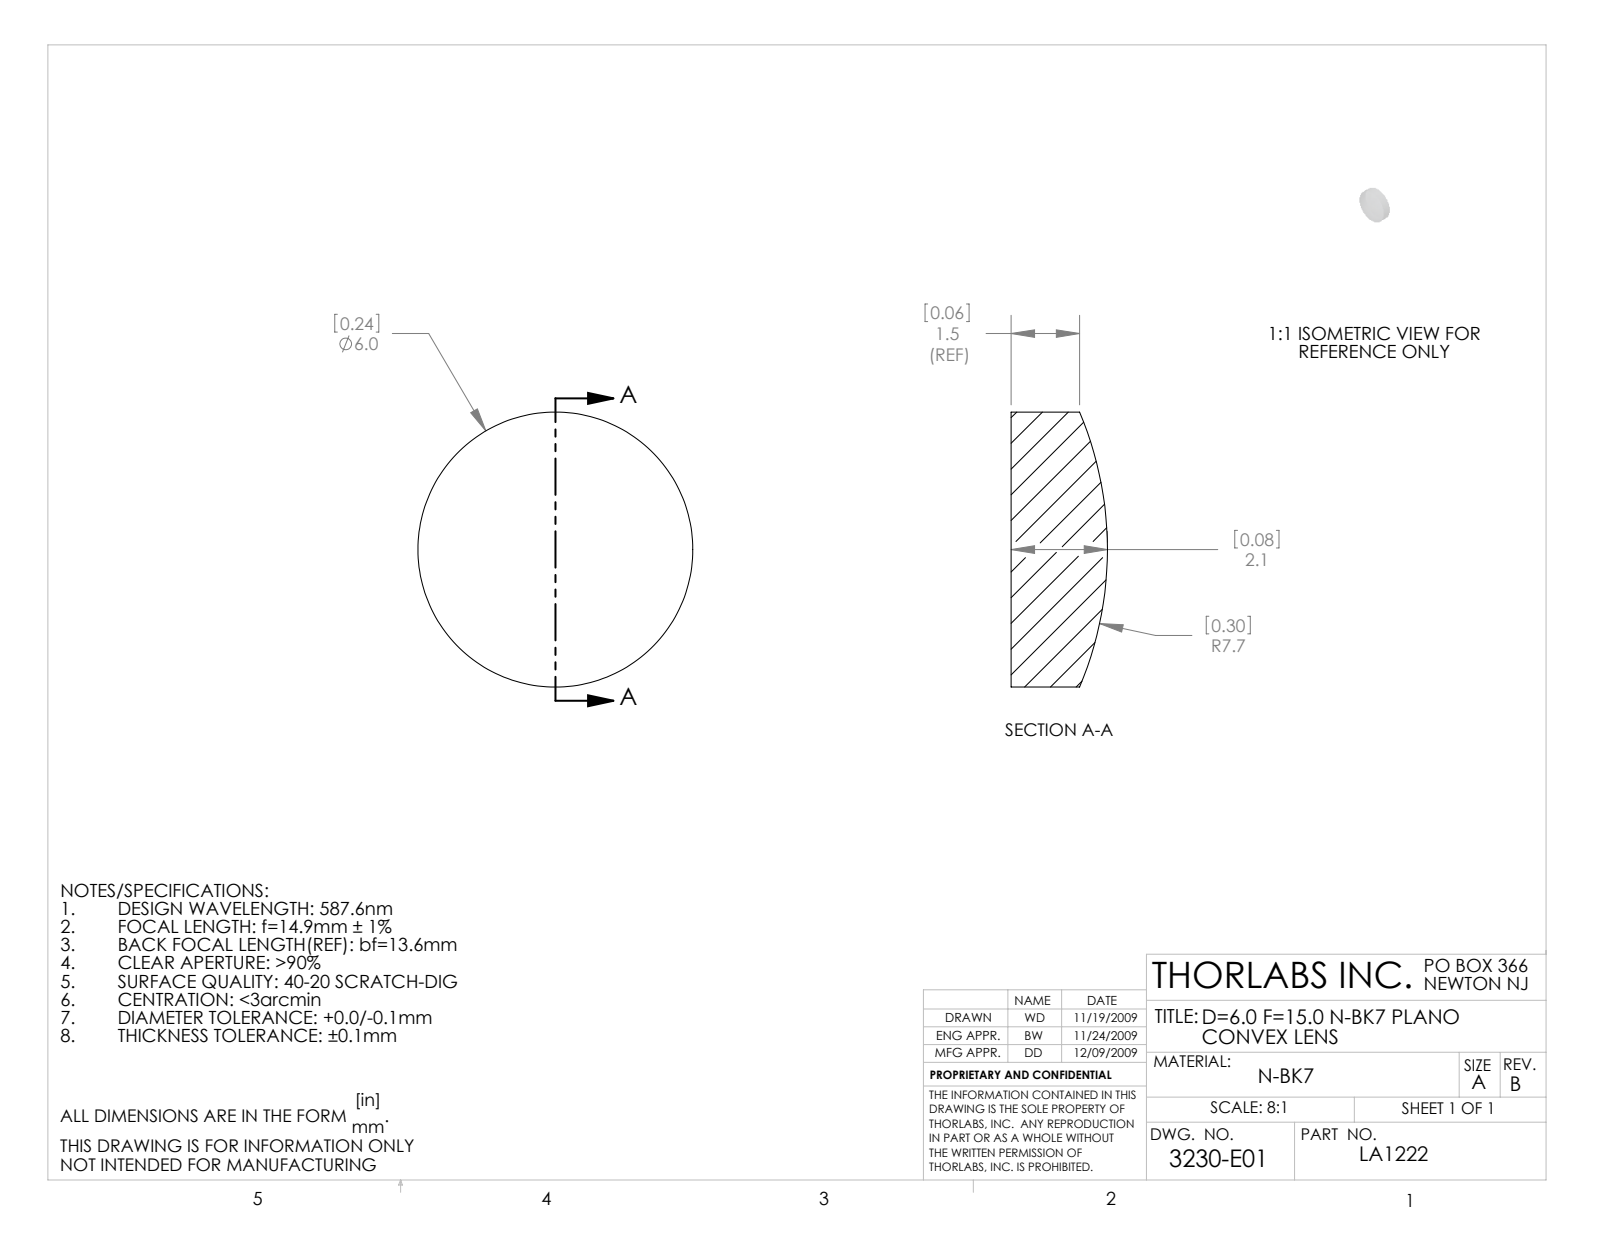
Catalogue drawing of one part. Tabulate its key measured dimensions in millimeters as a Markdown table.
| quantity | value |
| --- | --- |
| part name | 3230-E0W |
| STEP written by | SolidWorks 2009 (AUTOMOTIVE_DESIGN) |
| units | millimeters |
| bodies | 1 solid, 5 faces (1 planar, 2 cylindrical, 2 other) |
| overall size | 6 × 6 × 2.1 |
| volume | 51 mm³ |
| surface area | 86 mm² |
| round bosses / shafts (diameter × count) | 6 × 1 |
